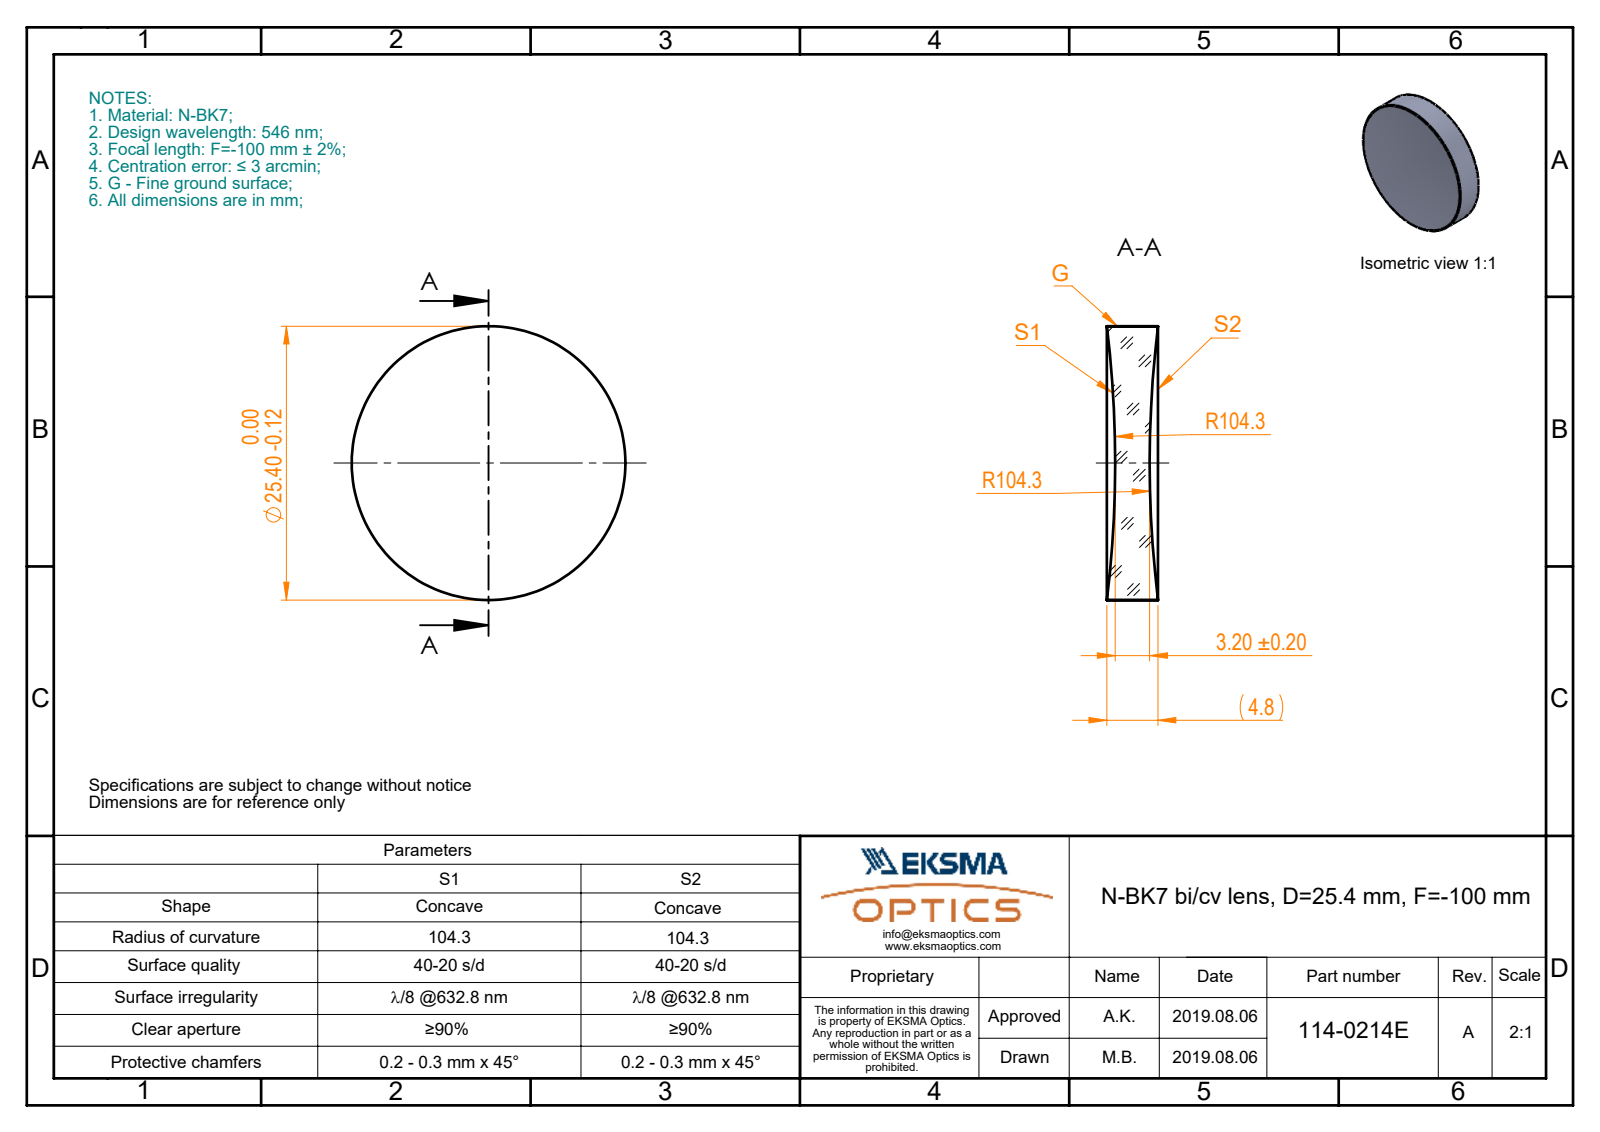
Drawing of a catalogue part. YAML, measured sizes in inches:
part_name: "114-0214E BK7 bi-cv 25.4 F-100"
step_written_by: "SolidWorks 2017 (CONFIG_CONTROL_DESIGN)"
units: inches
bodies: {solids: 1, faces: 6, planar: 0, cylindrical: 2, other: 4}
overall_size: [1, 1, 0.187]
volume: 0.123
surface_area: 2.164
round_bosses_or_shafts:
  - {diameter: 1, count: 1}
